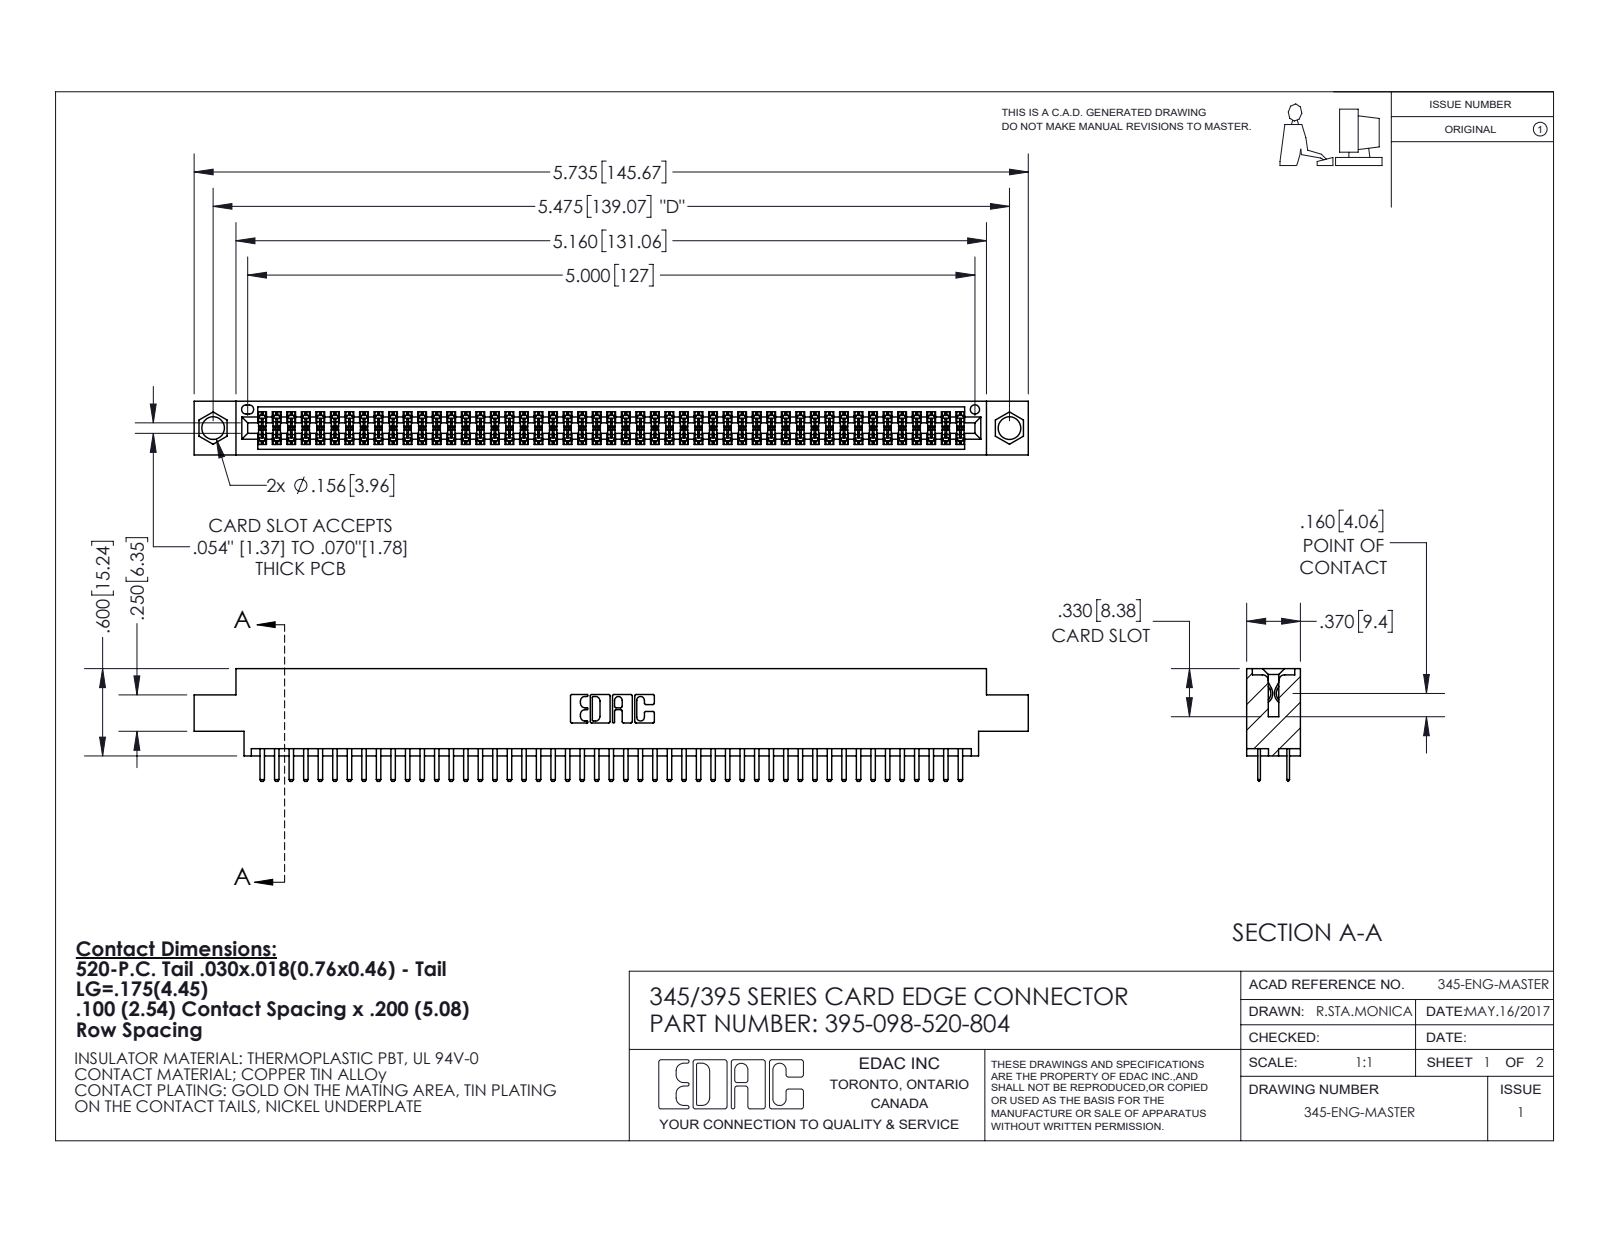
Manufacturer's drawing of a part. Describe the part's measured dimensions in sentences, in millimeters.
The part is named "395-098-520-804; 345-292-001_345-293-120; 345 Part_0.170 Offset - 0.156 Dia-TI". Its 3-D file was written by "SolidWorks 2020 (CONFIG_CONTROL_DESIGN)". It is 99 solids with 5436 faces: 3528 planar, 1908 cylindrical and 0 other. Overall it measures 145.7 by 19.7 by 9.4 millimeters. Its volume is 13 900 cubic millimeters and its surface area 20 660 square millimeters. Round holes: 2 of diameter 4, 1 of diameter 1.6. Partial cylindrical surfaces (rounded edges, fillets, slot ends): 196 of radius 0.2, 102 of radius 0.3, 22 of radius 0.3, 6 of radius 0.2, 6 of radius 0.8, 3 of radius 0.7, 2 of radius 0.4, 2 of radius 0.5. The main face-to-face distances are 1.8, 7.6, 5.1, 9.4, 2.5, 6.9, 0.6, 5.7, 0.6, 1.8. The hole center spacings are 6.9, 133.1, 139.1.
